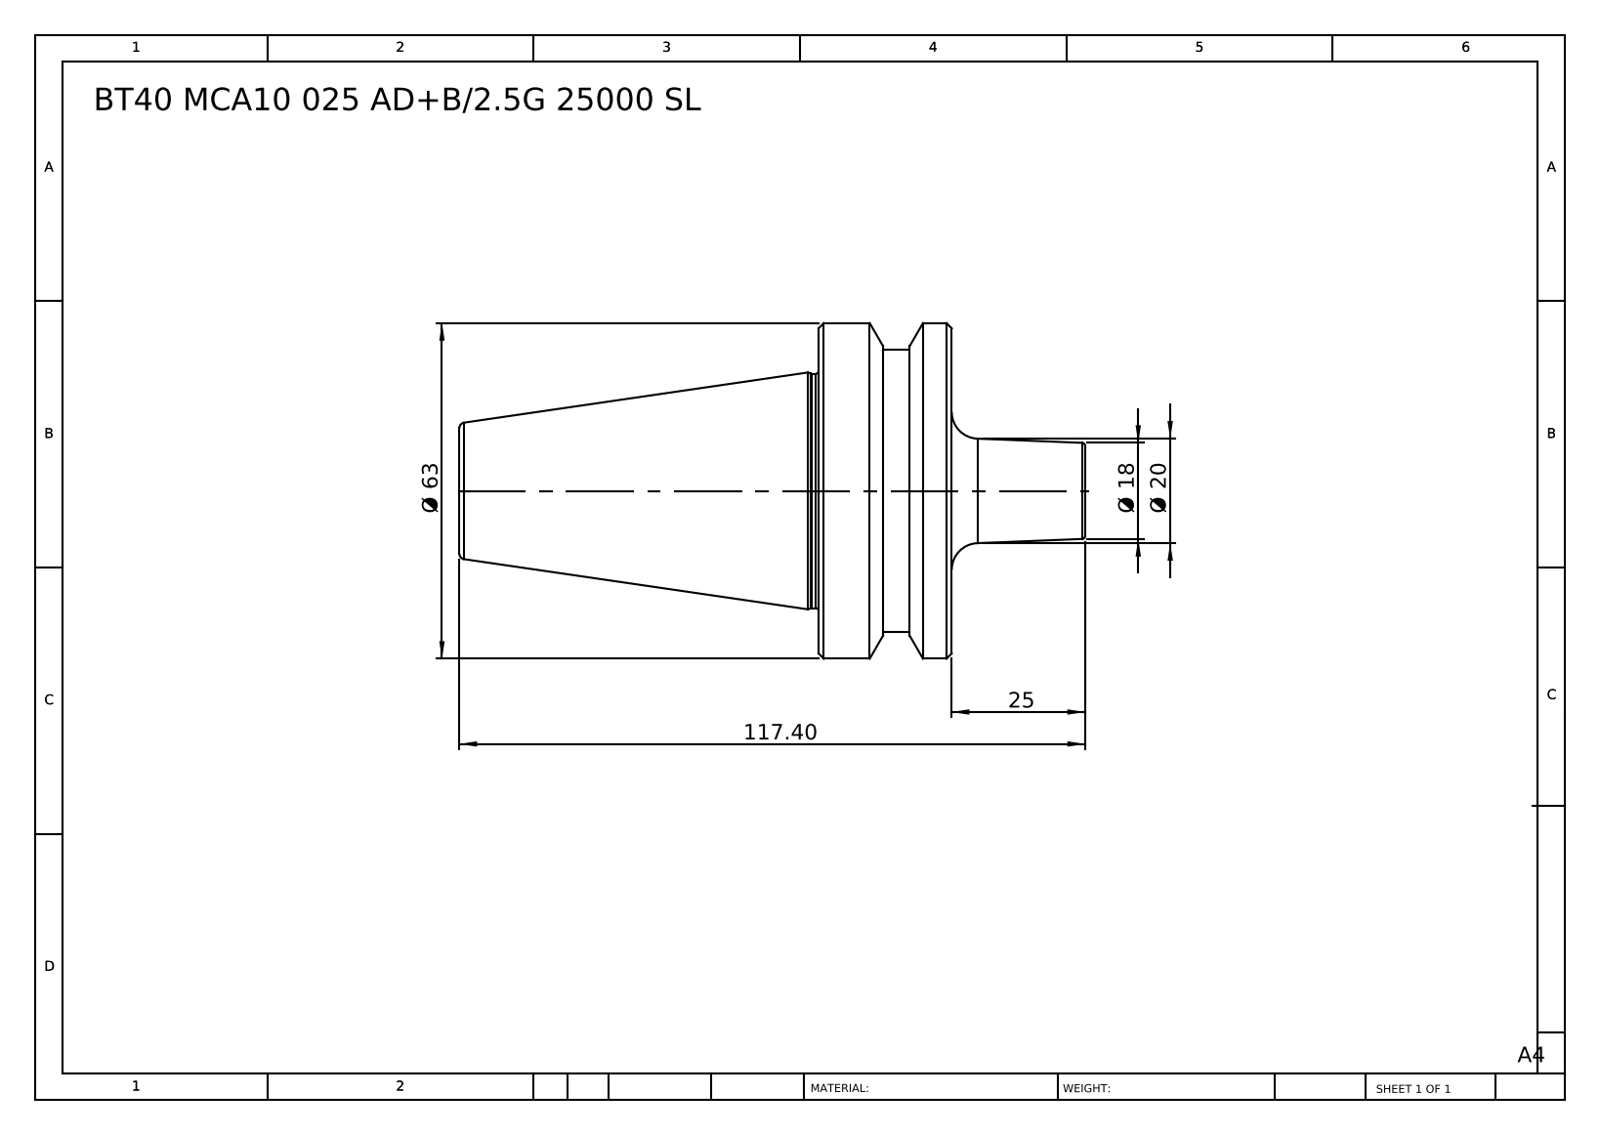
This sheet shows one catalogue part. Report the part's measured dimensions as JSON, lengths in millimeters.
{"part_name": "BT40 MCA10 025 AD+B-2.5G 25000 SL", "step_written_by": "SolidWorks 2014 (CONFIG_CONTROL_DESIGN)", "units": "millimeters", "bodies": {"solids": 1, "faces": 38, "planar": 6, "cylindrical": 8, "other": 24}, "overall_size": [117.4, 63, 63], "volume_mm3": 145777, "surface_area_mm2": 19643, "round_bosses_or_shafts": [[63, 1], [53, 1], [44, 1]], "face_to_face_distances": [25, 92.4, 67.4, 50, 117.4, 37.9, 12.9, 12.1, 79.5, 32.9]}
